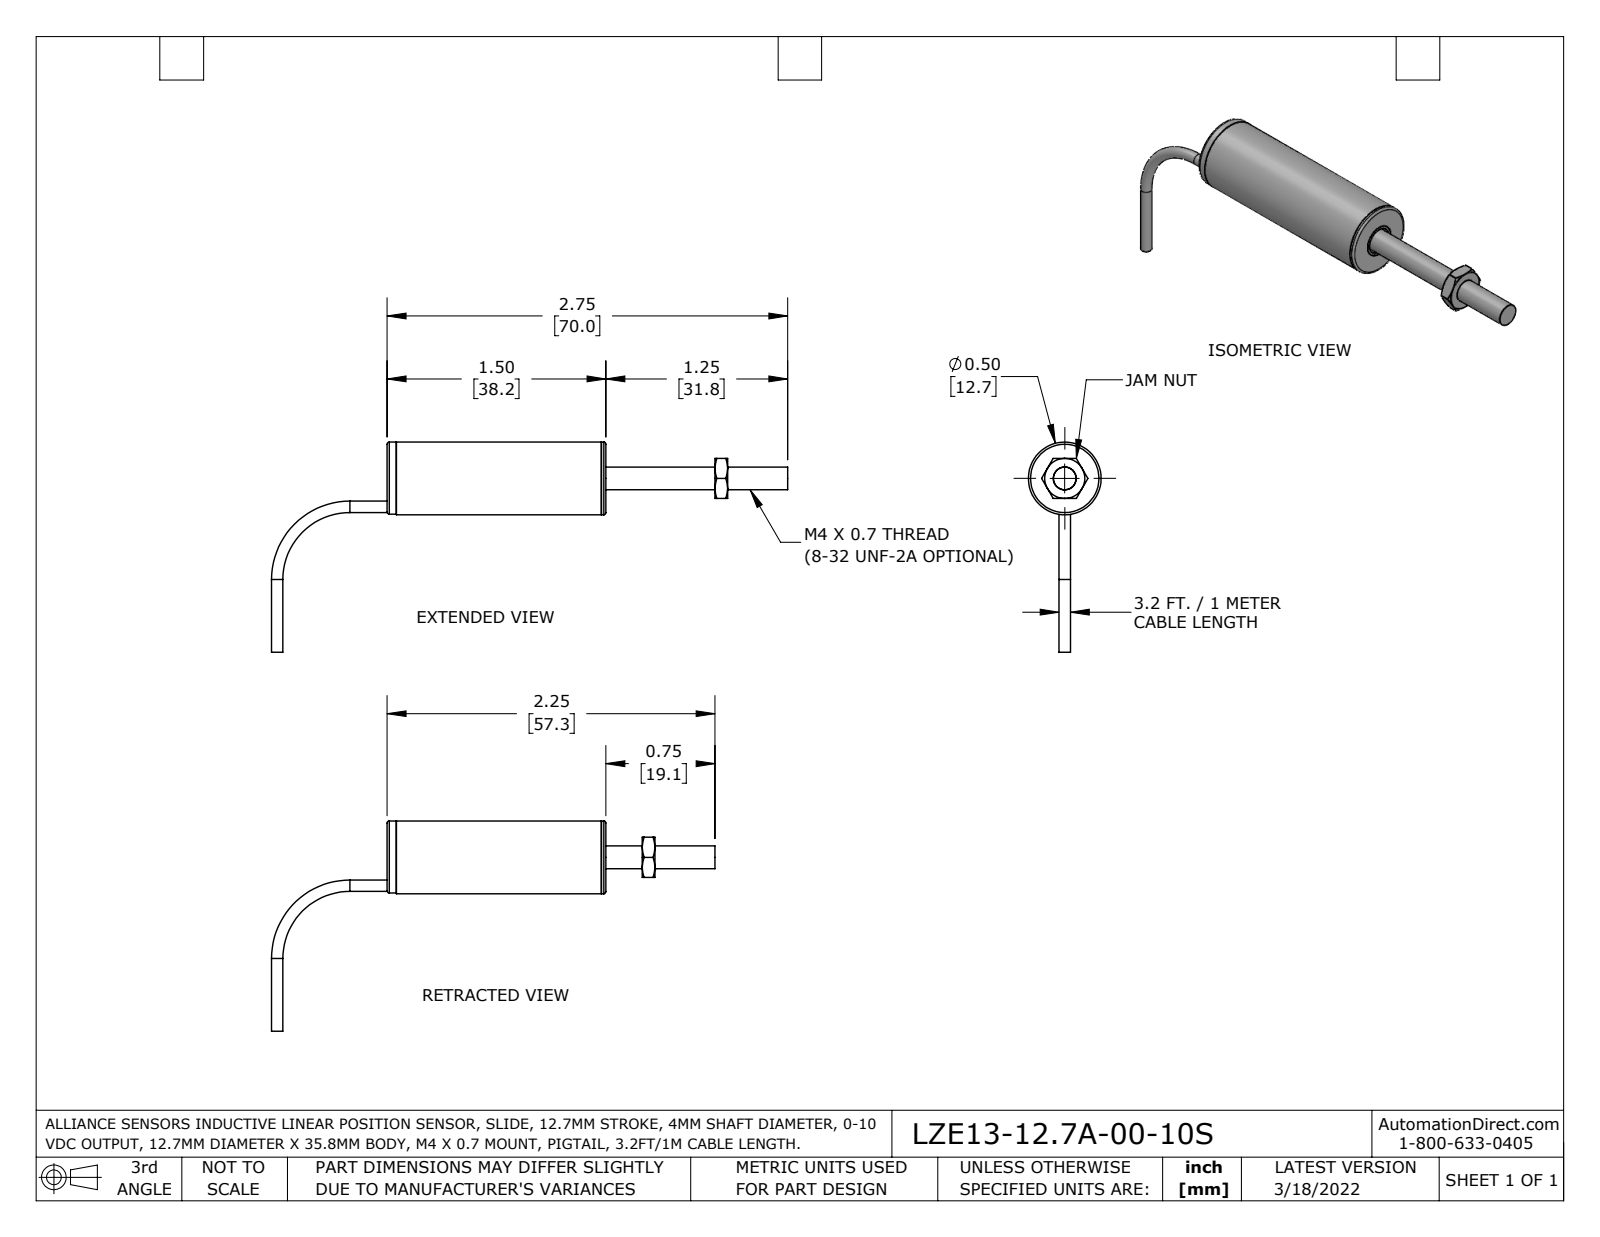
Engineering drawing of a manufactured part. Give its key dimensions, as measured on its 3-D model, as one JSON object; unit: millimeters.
{"part_name": "LZE13-12.7A-00-10S; 3120-0034-XX-Z_3120-0034-.50-Z; 3120-0040_SHRINK; 3300-0020-XX_3300-0020-.50 (+6 more)", "step_written_by": "SolidWorks 2021 (AUTOMOTIVE_DESIGN)", "units": "millimeters", "bodies": {"solids": 9, "faces": 98, "planar": 32, "cylindrical": 38, "other": 28}, "overall_size": [90.1, 36.7, 12.7], "volume_mm3": 2470, "surface_area_mm2": 6405, "round_holes": [[2, 1], [4, 1], [4.7, 1], [5.7, 1]], "round_bosses_or_shafts": [[12.7, 1], [11.9, 1], [5.6, 1], [4, 1], [2.5, 1], [2, 1]], "partial_cylinders_radius": [[1.2, 1]], "face_to_face_distances": [2, 1.6, 7, 2.4, 38.2, 36.6, 35.8, 34.2, 0.8, 19.1], "hole_center_spacings": [5]}
